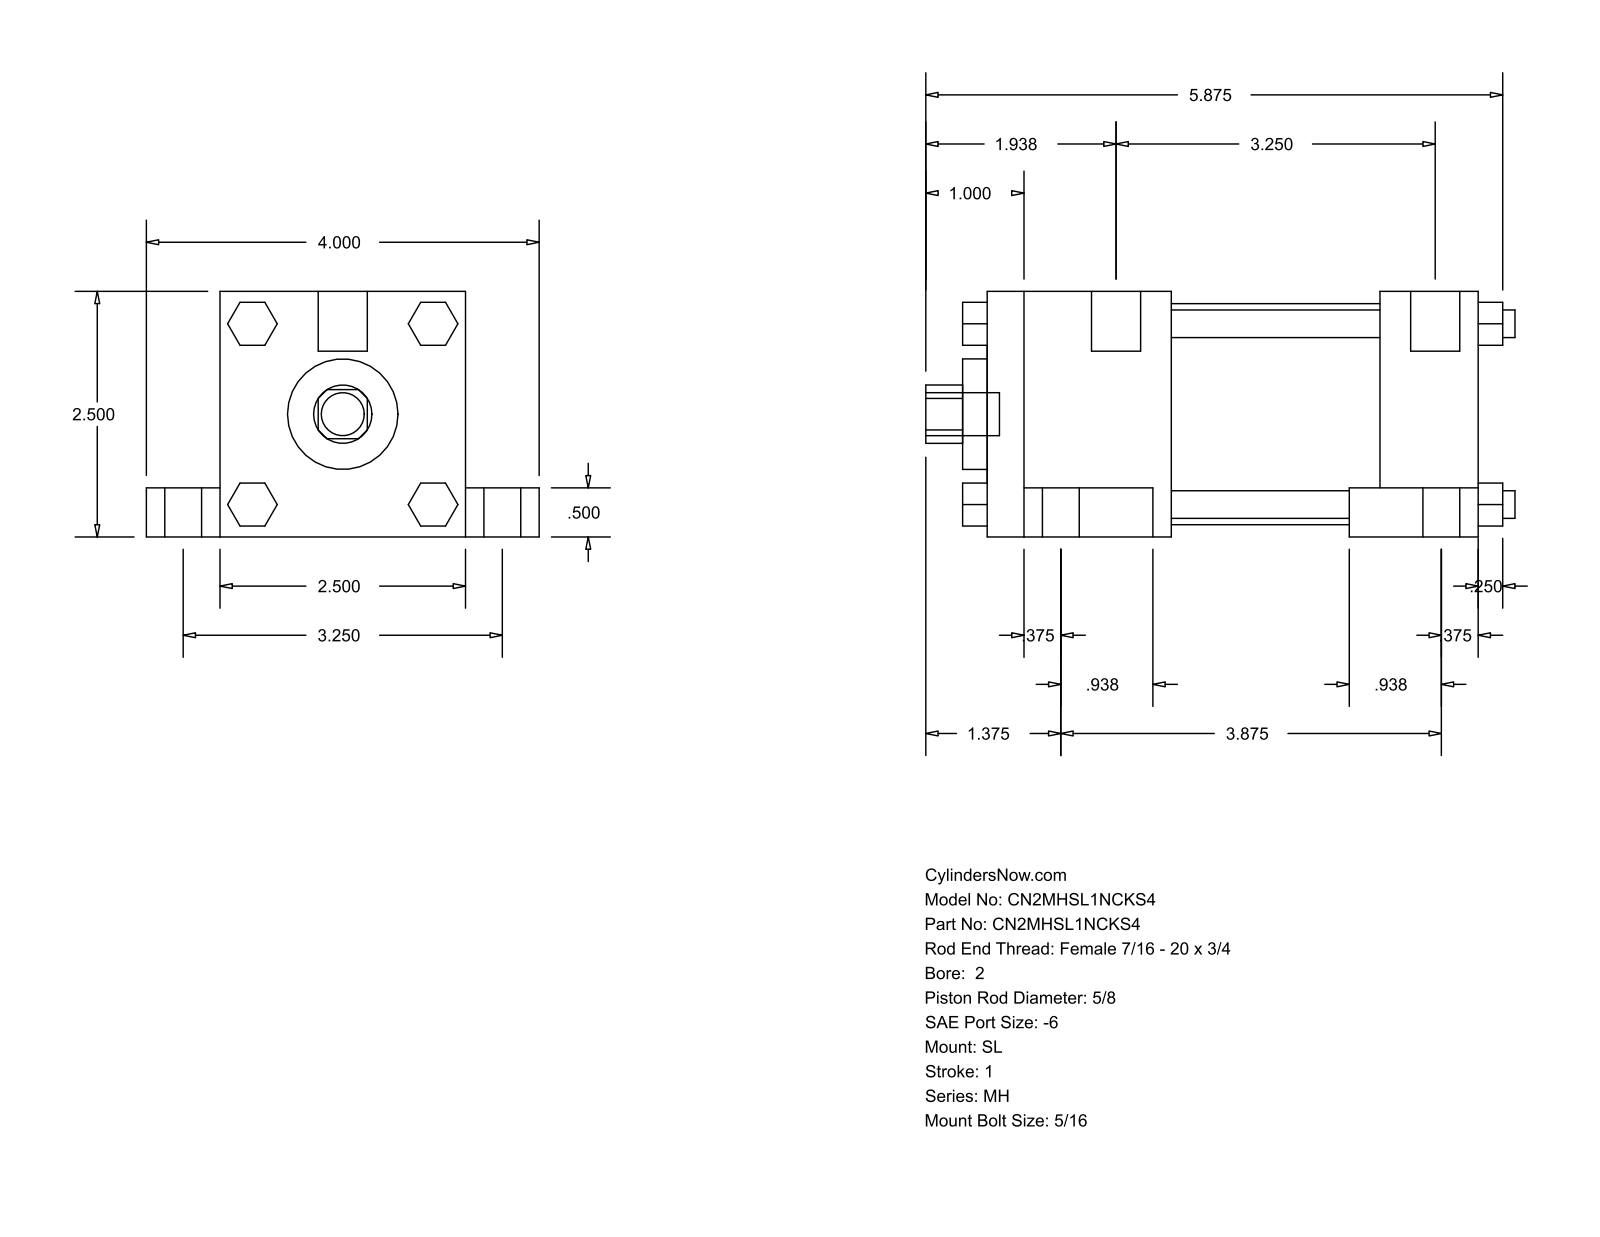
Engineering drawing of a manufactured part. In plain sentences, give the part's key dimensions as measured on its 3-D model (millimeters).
The part is named "MH_SL__0200_0.625". Its 3-D file was written by "GSSL Pune (CONFIG_CONTROL_DESIGN)". It is 0 solids with 148 faces: 112 planar, 36 cylindrical and 0 other. Overall it measures 152.4 by 101.6 by 63.5 millimeters. Round holes: 1 of diameter 15.88, 1 of diameter 28.57, 1 of diameter 57.15. Round bosses or shafts: 4 of diameter 15.88, 4 of diameter 9.53, 4 of diameter 7.14, 4 of diameter 5.56, 2 of diameter 12.7, 1 of diameter 11.11. Partial cylindrical surfaces (rounded edges, fillets, slot ends): 1 of radius 7.54. The main face-to-face distances are 63.5, 127, 50.8, 53.97, 12.7, 19.05, 82.55, 101.59, 25.41, 47.62.
